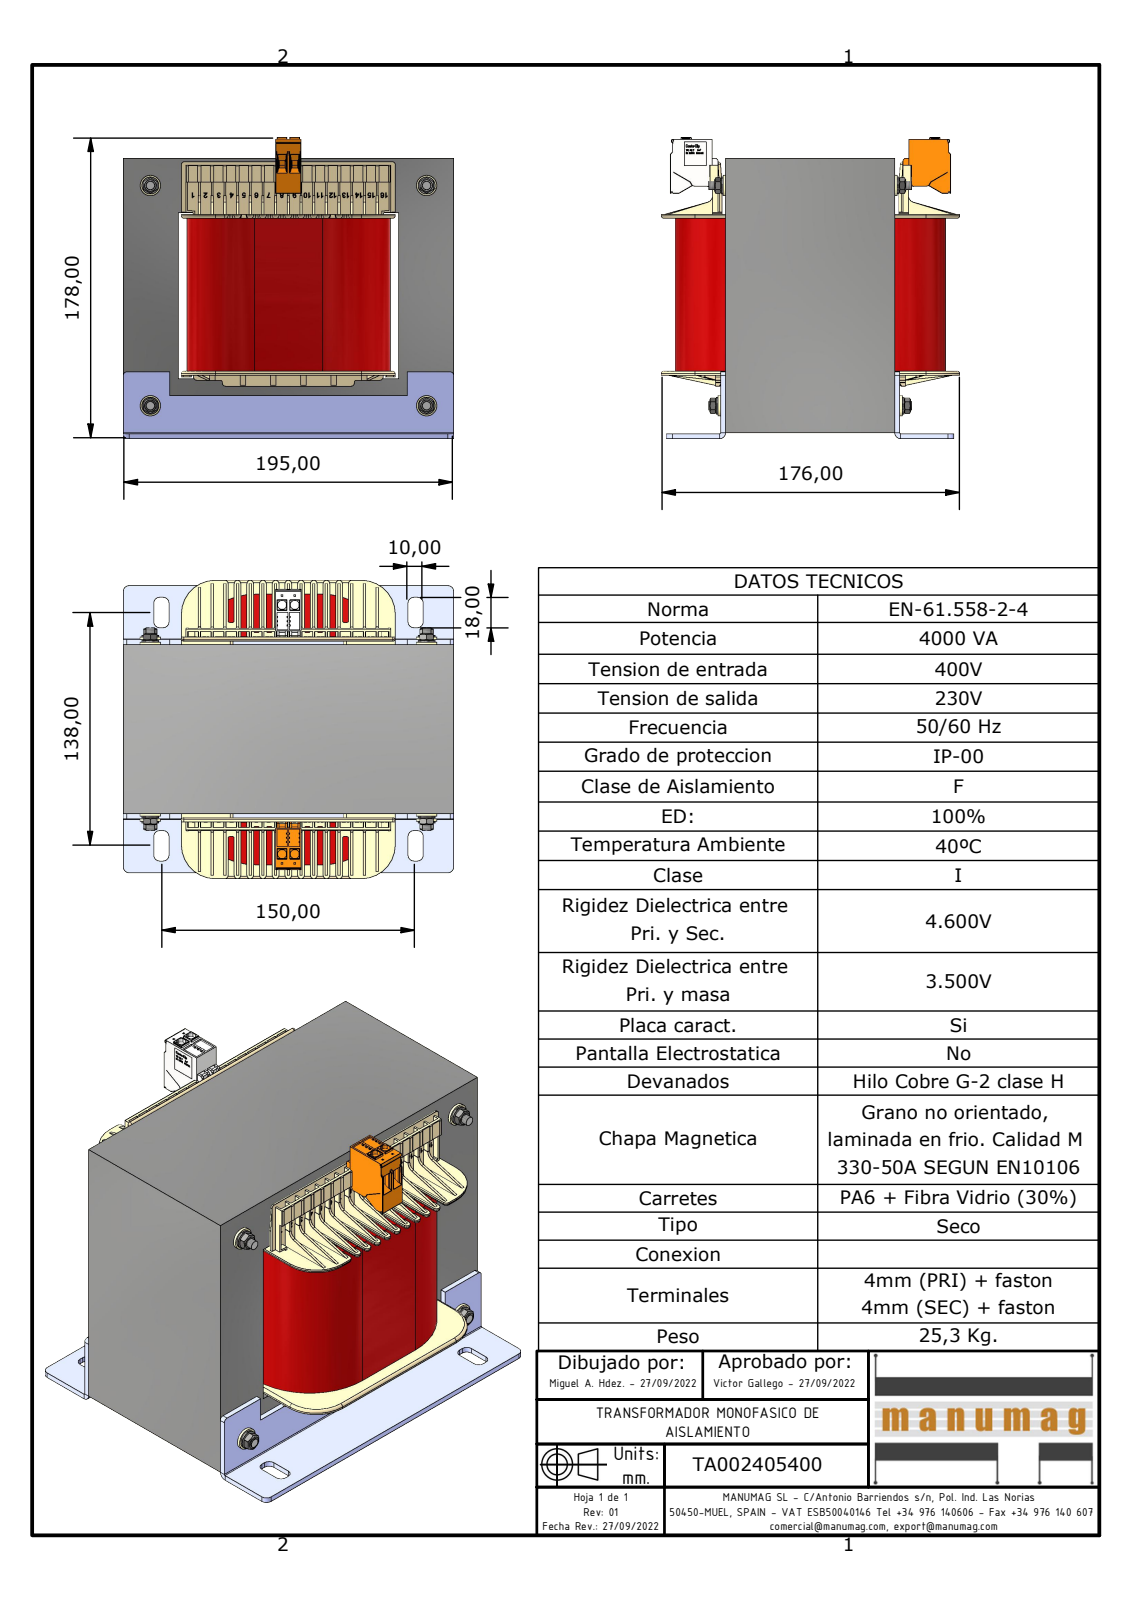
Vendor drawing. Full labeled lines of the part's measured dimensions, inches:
Part name (STEP PRODUCT): TA002405400; EI195 x 162 - 100 (Rc65); EI192_104_AK_25373_2_Wz837 BOBINADO; EI192_104_AK_25373_2_Wz837 (+8 more)
STEP written by: Autodesk Inventor 2023 (AUTOMOTIVE_DESIGN)
Units: inches
Bodies: 35 solids, 5978 faces (4008 planar, 708 cylindrical, 1262 other)
Overall size (bounding box): 7.677 × 7.008 × 6.953
Volume: 224.3 in³ · Surface area: 807.2 in²
Round holes (diameter × count): ⌀0.163 ×4, ⌀0.197 ×4, ⌀0.209 ×4, ⌀0.433 ×4, ⌀0.39 ×2
Round bosses / shafts (diameter × count): ⌀0.472 ×4, ⌀0.394 ×4, ⌀0.232 ×4
Partial cylindrical surfaces — rounded edges, fillets, slot ends (radius × count): R0.006 ×146, R0.008 ×64, R0.039 ×52, R0.059 ×44, R0.02 ×28, R0.077 ×22, R0.138 ×22, R0.012 ×12
Main face-to-face distances: 1.28, 5.118, 0.118, 6.398, 0.094, 3.937, 2.559, 3.646, 0.079, 3.839
Hole centre spacings: 5.118, 6.417, 8.208
